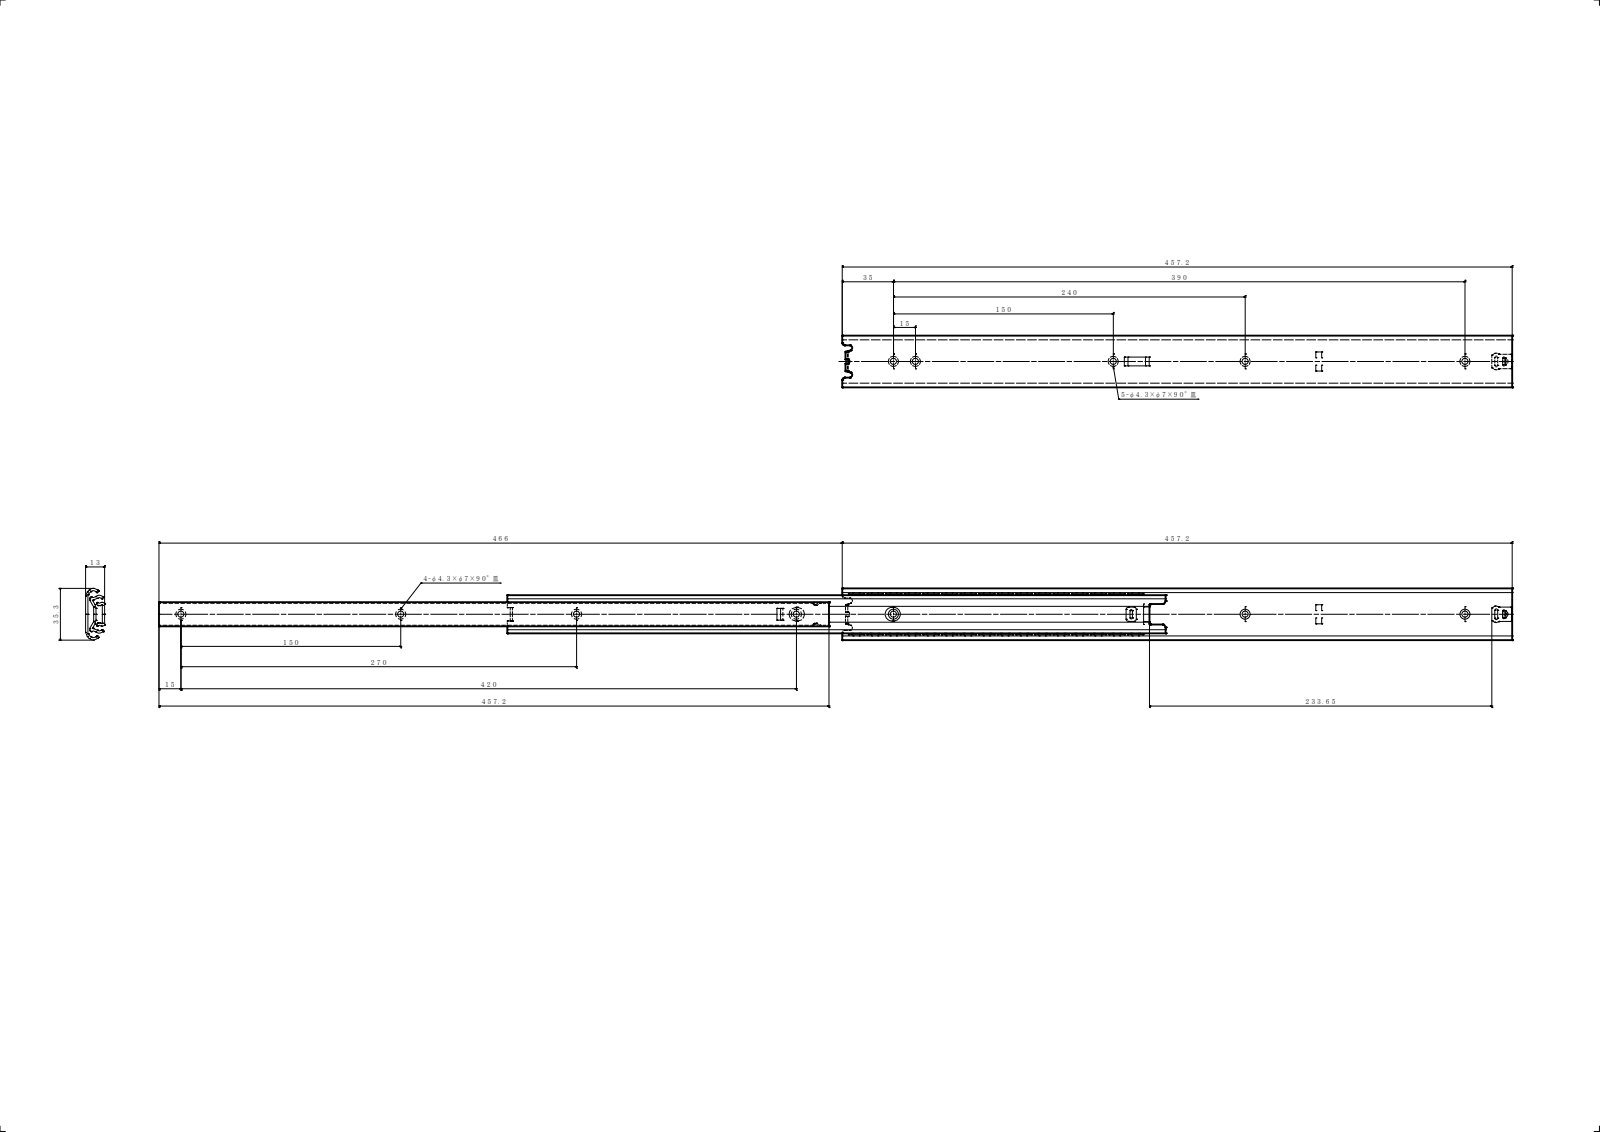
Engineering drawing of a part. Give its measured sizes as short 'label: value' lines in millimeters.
name: PN32; PN36; C351-18 OM; C351-18 (+2 more)
written by: SolidWorks 2019 (CONFIG_CONTROL_DESIGN)
unit: mm
bodies: 5 solids, 296 faces (144 planar, 132 cylindrical, 20 other)
size: 923.46 × 35.3 × 13
volume: 80 089 mm³; area: 103 935 mm²
holes: 9× ⌀4.3, 1× ⌀4.5
rounds: 21× R0.5, 8× R1.5, 8× R2, 6× R0.3, 4× R0.8, 4× R1, 4× R1.6, 4× R2.38
face distances: 1.6, 11.4, 5.4, 6, 13, 9.8, 3.8, 7.6, 7, 4.4
hole spacings: 150, 216.26, 240, 270, 456.26, 486.26, 726.26, 15
